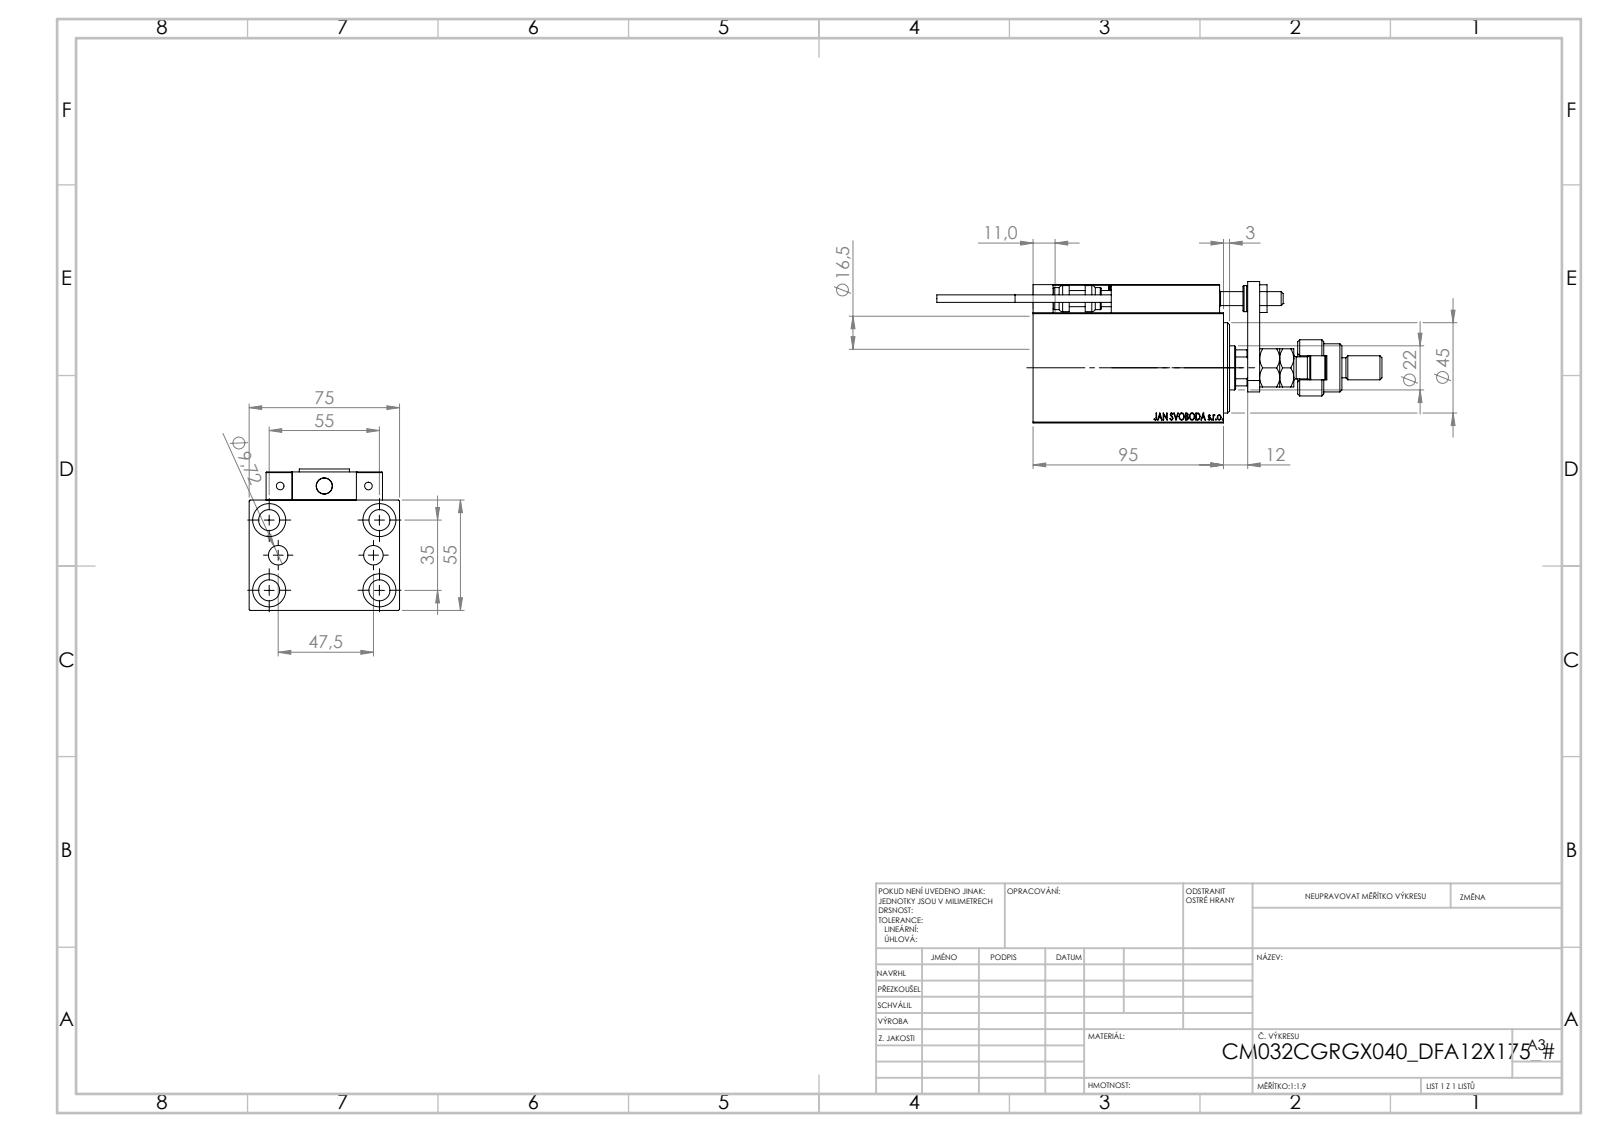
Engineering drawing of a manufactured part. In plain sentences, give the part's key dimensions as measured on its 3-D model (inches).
The part is named "X_Y_DFA; NUT_D12; SWITCH X; FEMALE_PART_FOR_DFA (+8 more)". Its 3-D file was written by "SolidWorks 2019 (CONFIG_CONTROL_DESIGN)". It is 25 solids with 1363 faces: 588 planar, 197 cylindrical and 578 other. Overall it measures 8.74 by 2.953 by 2.776 inches. Its volume is 24.38 cubic inches and its surface area 155.2 square inches. Round holes: 6 of diameter 0.157, 5 of diameter 0.315, 5 of diameter 0.413, 5 of diameter 0.65, 4 of diameter 0.126, 2 of diameter 0.197, 2 of diameter 0.383, 1 of diameter 0.276, 1 of diameter 0.866, 1 of diameter 1.004, 1 of diameter 1.26, 1 of diameter 1.339. Round bosses or shafts: 2 of diameter 0.433, 2 of diameter 0.197, 2 of diameter 0.15, 1 of diameter 1.102, 1 of diameter 0.945, 1 of diameter 0.709, 1 of diameter 0.512, 1 of diameter 0.472. Partial cylindrical surfaces (rounded edges, fillets, slot ends): 30 of radius 0.012, 2 of radius 0.118, 1 of radius 0.384, 1 of radius 0.413. The main face-to-face distances are 2.165, 2.953, 0.551, 0.197, 2.717, 0.709, 0.984, 0.236, 1.772, 0.472. The hole center spacings are 0.705, 1.283, 2.132, 0.448, 0.787, 0.935, 1.165, 1.169.
